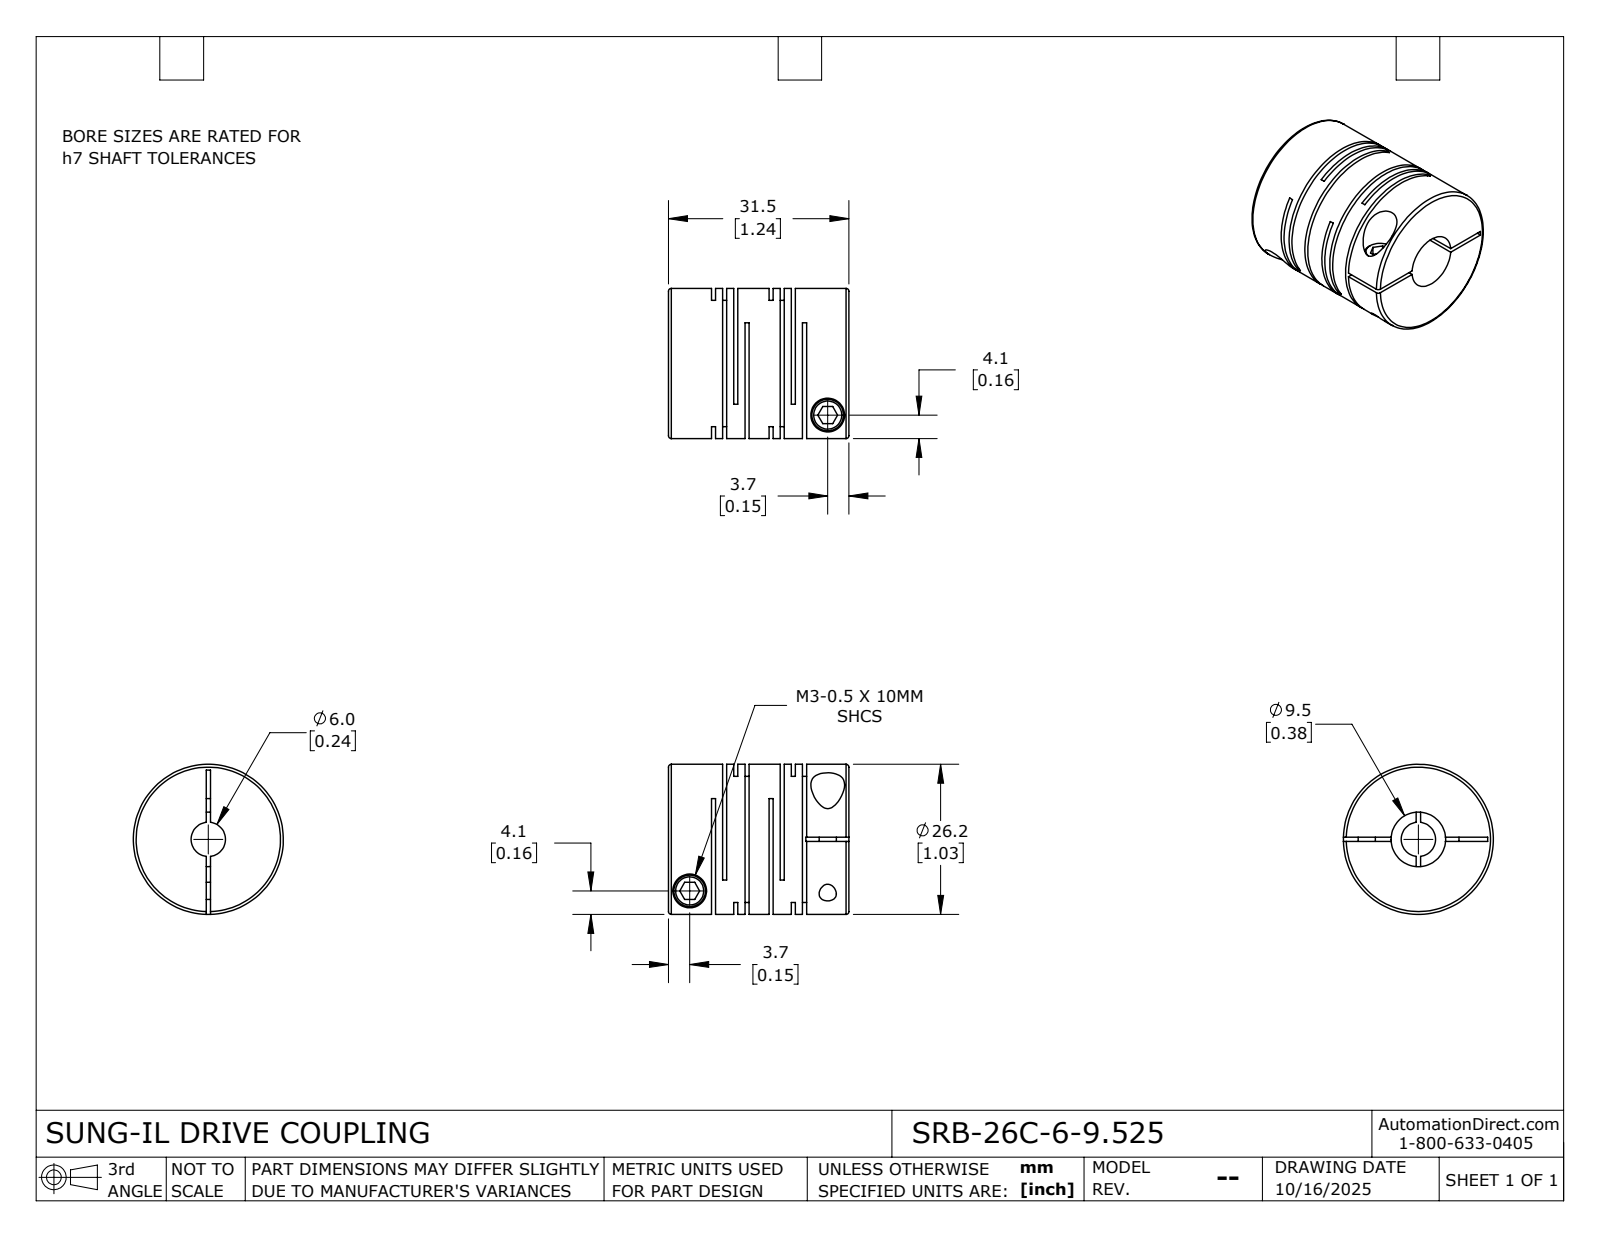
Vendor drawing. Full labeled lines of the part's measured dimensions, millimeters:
Part name (STEP PRODUCT): SRB-26C-6-9.525
STEP written by: SolidWorks 2024 (CONFIG_CONTROL_DESIGN)
Units: millimetres
Bodies: 1 solid, 115 faces (60 planar, 42 cylindrical, 13 other)
Overall size (bounding box): 31.5 × 26.2 × 26.2
Volume: 12 427 mm³ · Surface area: 10 879 mm²
Round holes (diameter × count): ⌀3 ×2, ⌀5.9 ×2, ⌀6 ×1, ⌀9.53 ×1
Round bosses / shafts (diameter × count): ⌀5.5 ×2, ⌀26.2 ×1
Main face-to-face distances: 1.95, 10.05, 0.71, 3.9, 8.1, 12, 1.24, 2.66, 9.34, 13.95
